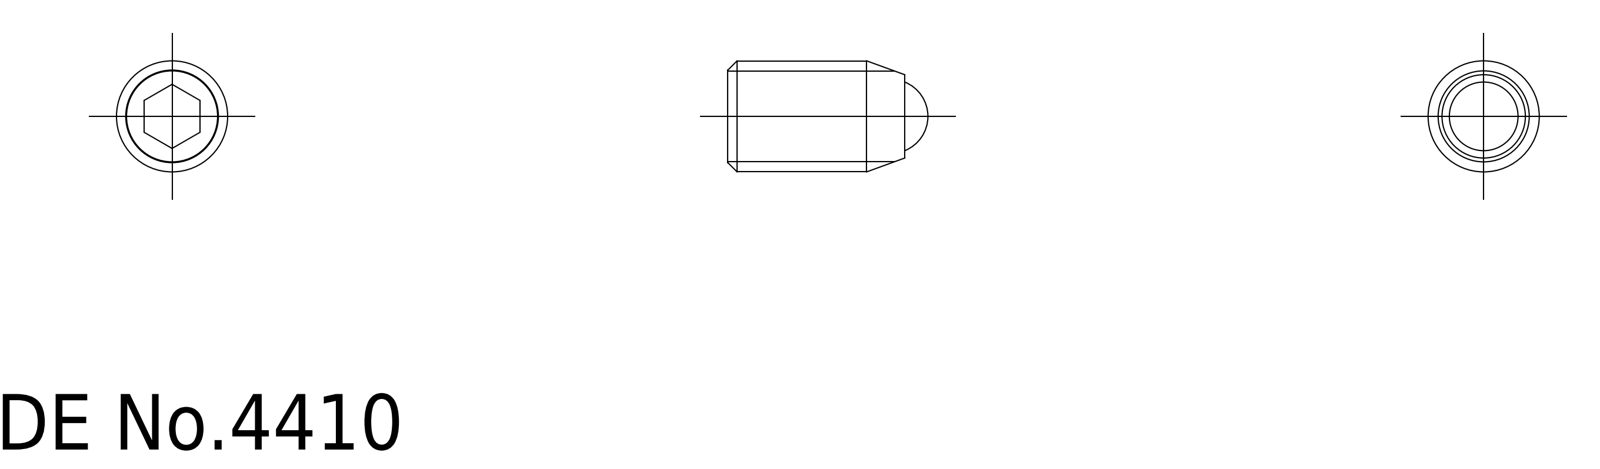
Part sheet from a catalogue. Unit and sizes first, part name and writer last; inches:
Units: inches
Overall size (bounding box): 0.425 × 0.236 × 0.236
Volume: 0.013 in³ · Surface area: 0.555 in²
Bodies: 2 solids, 20 faces (0 planar, 0 cylindrical, 20 other)
Part name (STEP PRODUCT): ball; SCSS_M6_10_R_19014_36
STEP written by: CADfix (AUTOMOTIVE_DESIGN)
